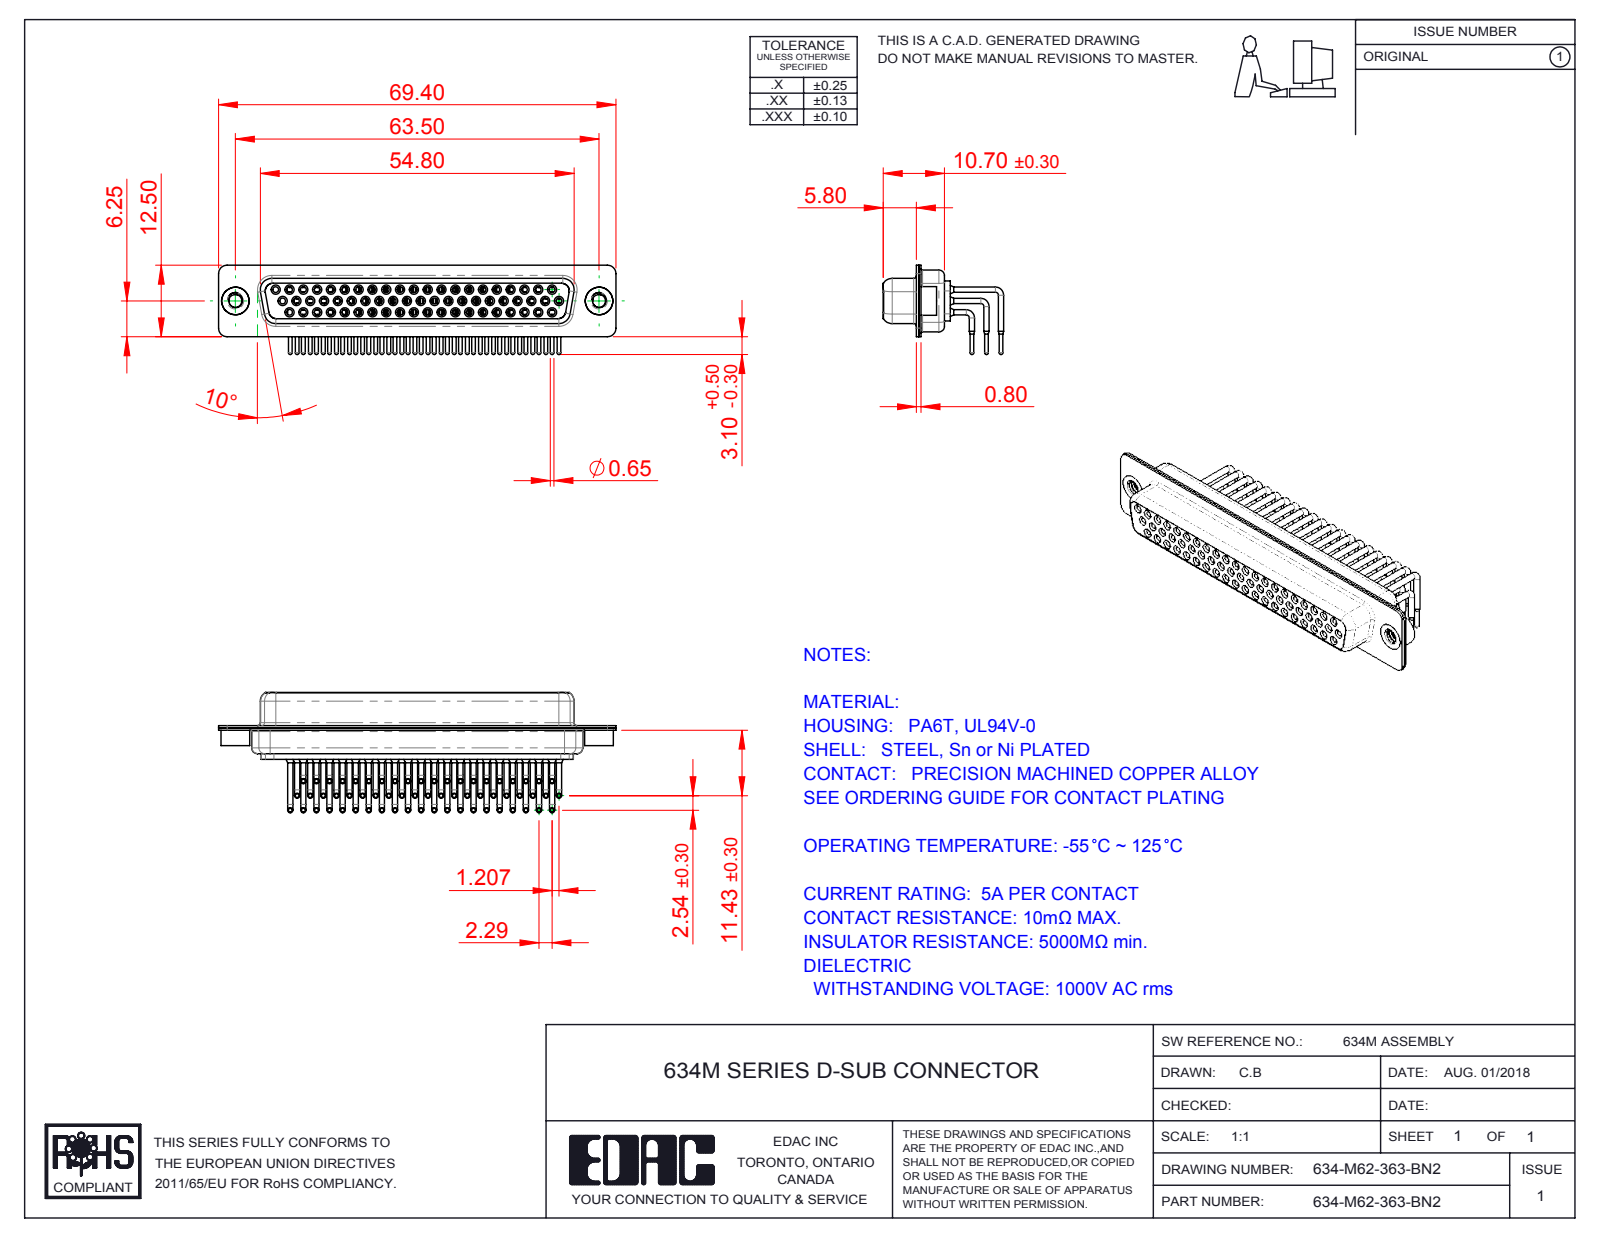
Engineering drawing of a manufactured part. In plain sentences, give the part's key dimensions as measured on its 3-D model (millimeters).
The part is named "634M Housing_62 Contacts; 634M Contact Row 2; 634M Contact Row 1; 634M Contact Row 3 (+4 more)". Its 3-D file was written by "SolidWorks 2016 (CONFIG_CONTROL_DESIGN)". It is 67 solids with 3565 faces: 997 planar, 1563 cylindrical and 1005 other. Overall it measures 69.4 by 21.02 by 15.6 millimeters. Its volume is 5 405 cubic millimeters and its surface area 17 868 square millimeters. Round holes: 62 of diameter 1, 62 of diameter 1.1, 62 of diameter 1.7, 62 of diameter 1.8, 62 of diameter 2, 2 of diameter 2.26, 2 of diameter 4, 2 of diameter 4.8. Round bosses or shafts: 124 of diameter 0.9, 62 of diameter 1.6, 62 of diameter 1.5, 62 of diameter 0.65, 56 of diameter 2, 2 of diameter 5, 2 of diameter 4.9. Partial cylindrical surfaces (rounded edges, fillets, slot ends): 16 of radius 1.5, 12 of radius 2, 8 of radius 1.35, 8 of radius 1.6, 4 of radius 0.25, 4 of radius 0.5, 4 of radius 0.6, 4 of radius 0.65. The main face-to-face distances are 0.4, 1.45, 8.95, 1.9, 8.5, 2.3, 6.2, 0.45, 7.05, 0.85. The hole center spacings are 7.24, 2.32, 2.41, 9.65, 4.13, 4.83, 16.89, 14.48.
